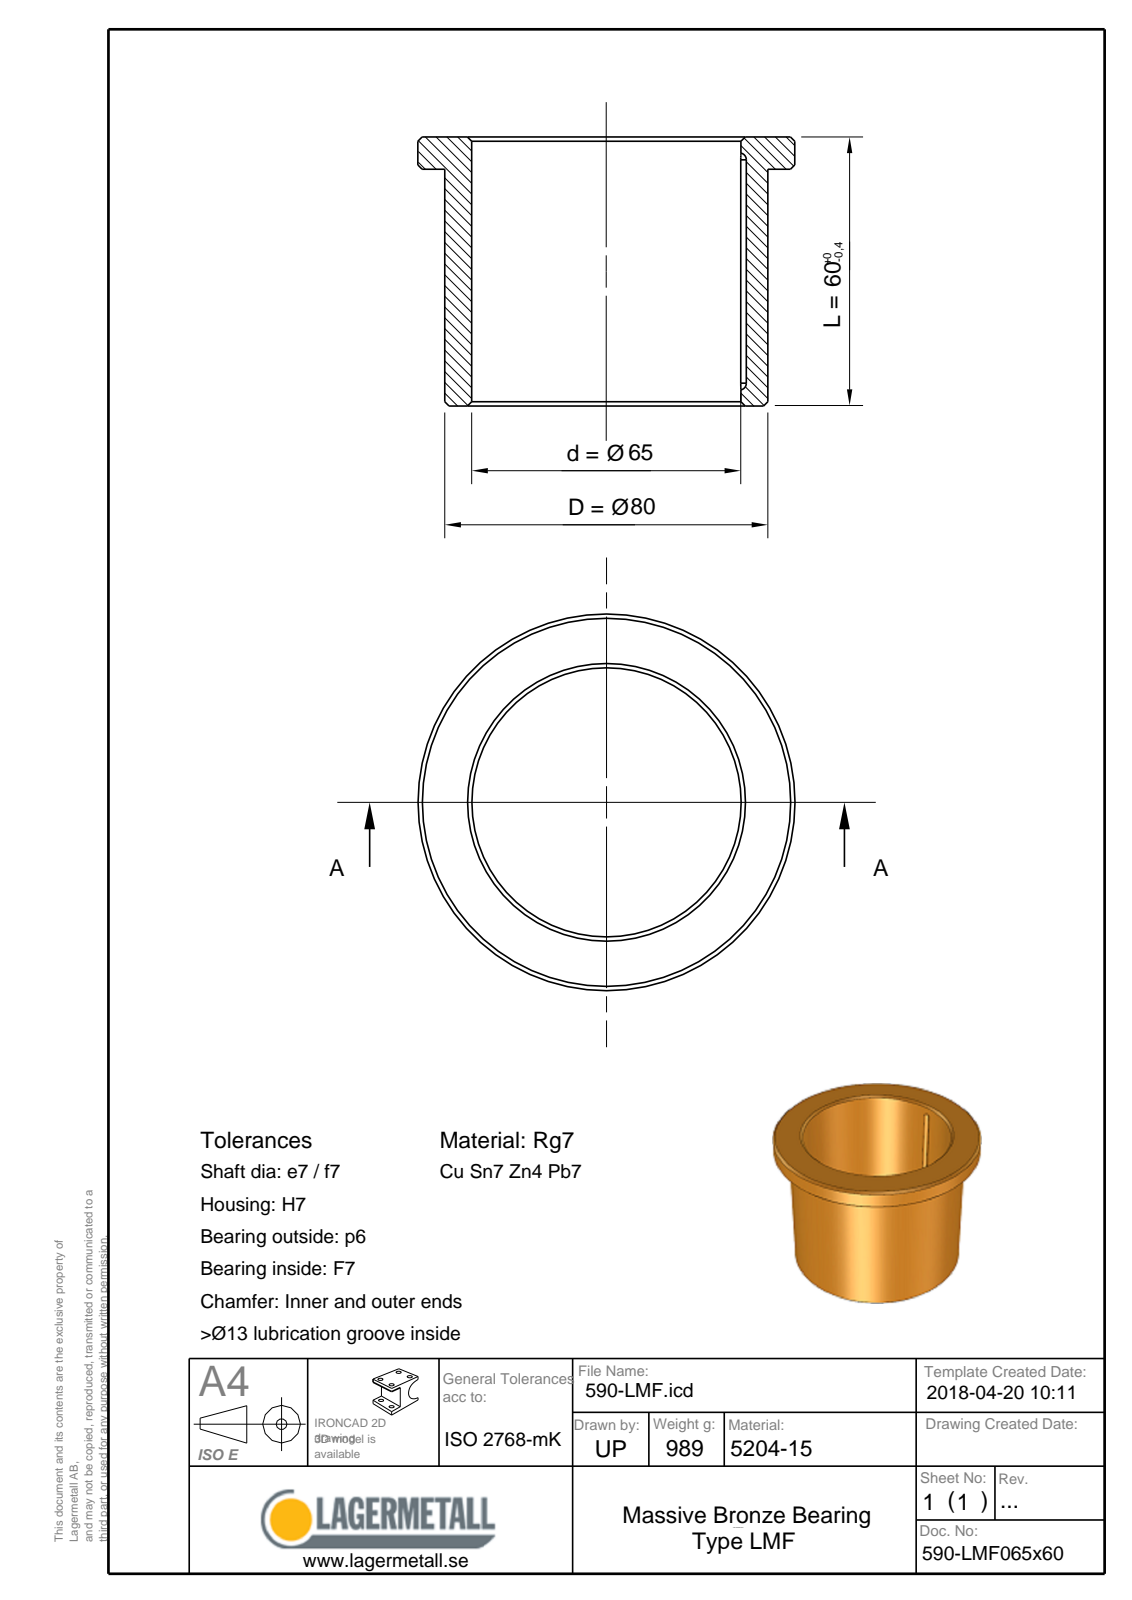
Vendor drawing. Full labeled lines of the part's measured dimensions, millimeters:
Part name (STEP PRODUCT): 590-LMF065x60
STEP written by: Spatial InterOp 3D (CONFIG_CONTROL_DESIGN)
Units: millimetres
Bodies: 1 solid, 16 faces (4 planar, 5 cylindrical, 7 other)
Overall size (bounding box): 90 × 90 × 60
Volume: 112 360 mm³ · Surface area: 33 037 mm²
Round holes (diameter × count): ⌀65 ×1
Round bosses / shafts (diameter × count): ⌀90 ×1, ⌀80 ×1
Partial cylindrical surfaces — rounded edges, fillets, slot ends (radius × count): R1.75 ×2
Main face-to-face distances: 60, 52, 8
